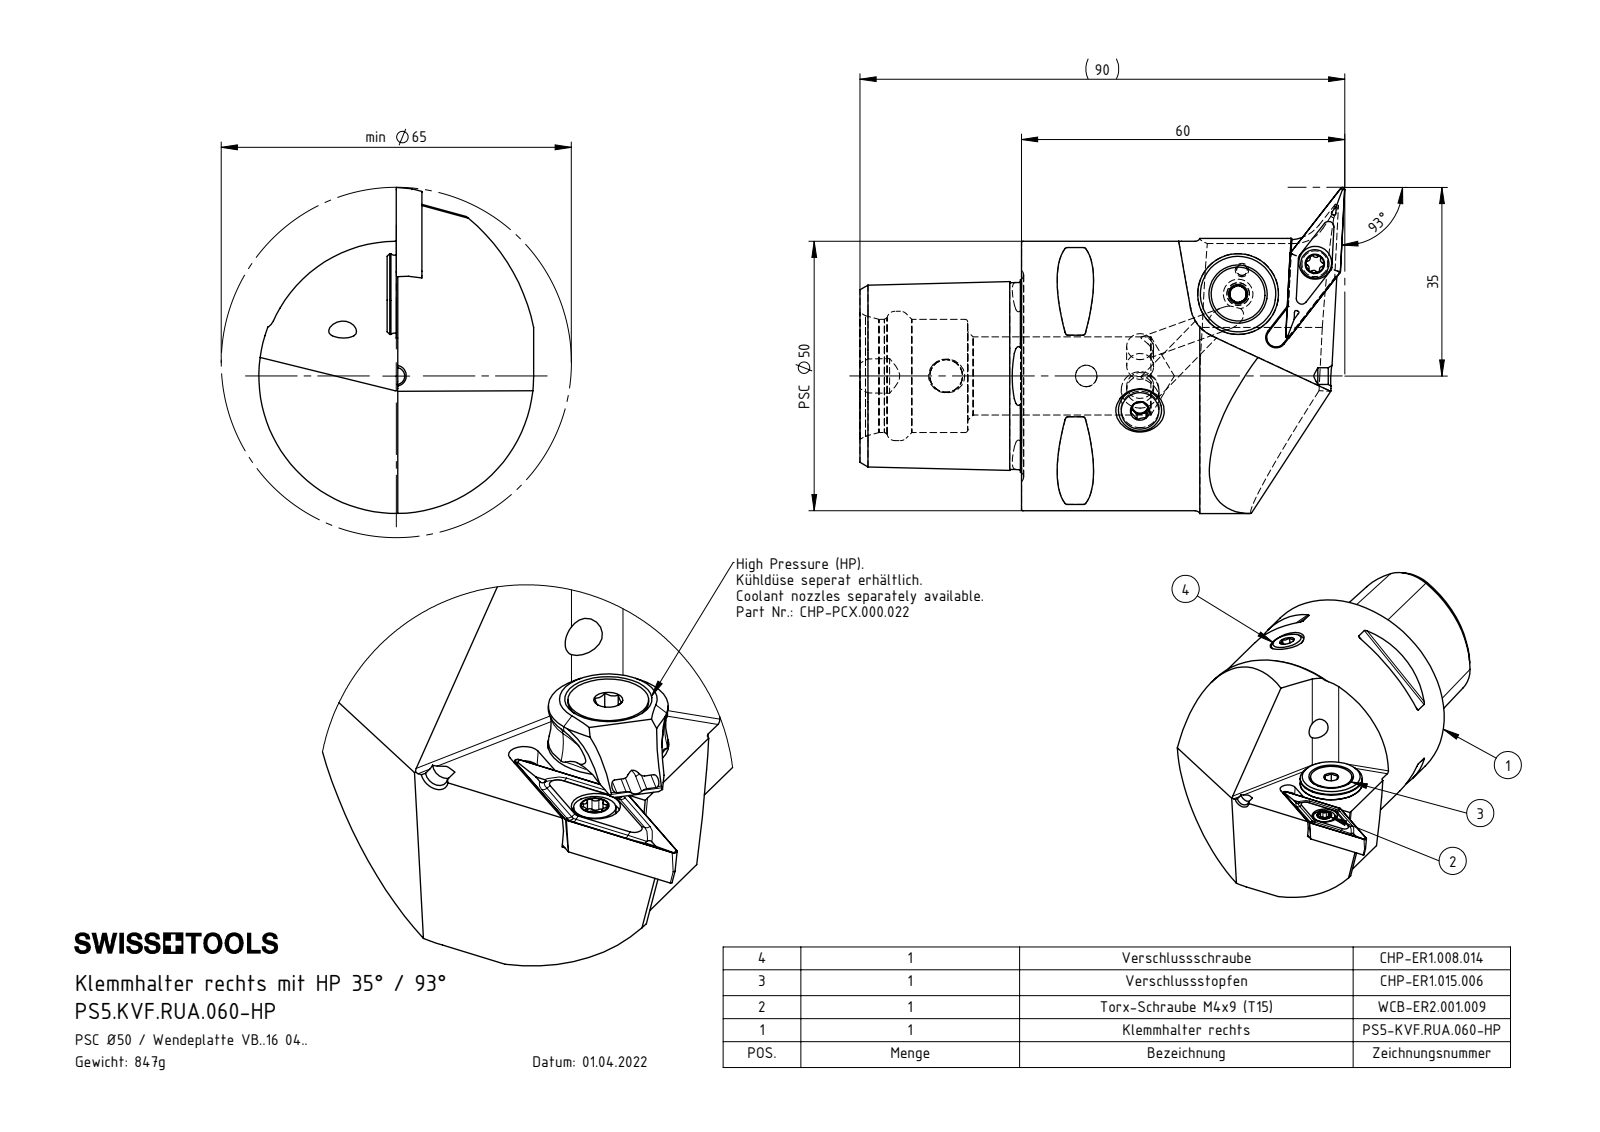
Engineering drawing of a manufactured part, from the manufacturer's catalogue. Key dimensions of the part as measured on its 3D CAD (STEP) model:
Part name (STEP PRODUCT): CHP-PCX.000.022_Dse; CHP-PCX.000.022_B; DIN 7991 - M5x18; ISO 8752 2x8 (+7 more)
STEP written by: SolidWorks 2017 (AUTOMOTIVE_DESIGN)
Units: millimetres
Bodies: 9 solids, 488 faces (106 planar, 137 cylindrical, 245 other)
Overall size (bounding box): 90 × 60.5 × 51
Volume: 107 913 mm³ · Surface area: 23 729 mm²
Round holes (diameter × count): ⌀4.2 ×2, ⌀5 ×2, ⌀6.1 ×2, ⌀1.2 ×1, ⌀2 ×1, ⌀3 ×1, ⌀3.3 ×1, ⌀4 ×1, ⌀4.4 ×1, ⌀5.3 ×1, ⌀7 ×1, ⌀13 ×1
Round bosses / shafts (diameter × count): ⌀50 ×1, ⌀14.85 ×1, ⌀13.4 ×1, ⌀10 ×1, ⌀8 ×1, ⌀5.5 ×1, ⌀5.25 ×1, ⌀5 ×1
Partial cylindrical surfaces — rounded edges, fillets, slot ends (radius × count): R0.5 ×12, R1 ×7, R0.34 ×6, R0.59 ×6, R6 ×3, R0.15 ×2, R1.1 ×2, R1.2 ×2
Main face-to-face distances: 30, 4.46, 20.74, 25.2, 19.18, 20.7, 4.5, 44.4, 1.5, 3
Hole centre spacings: 4.5, 13.59, 13.69, 15.31, 15.45, 26, 32.04, 34.95
